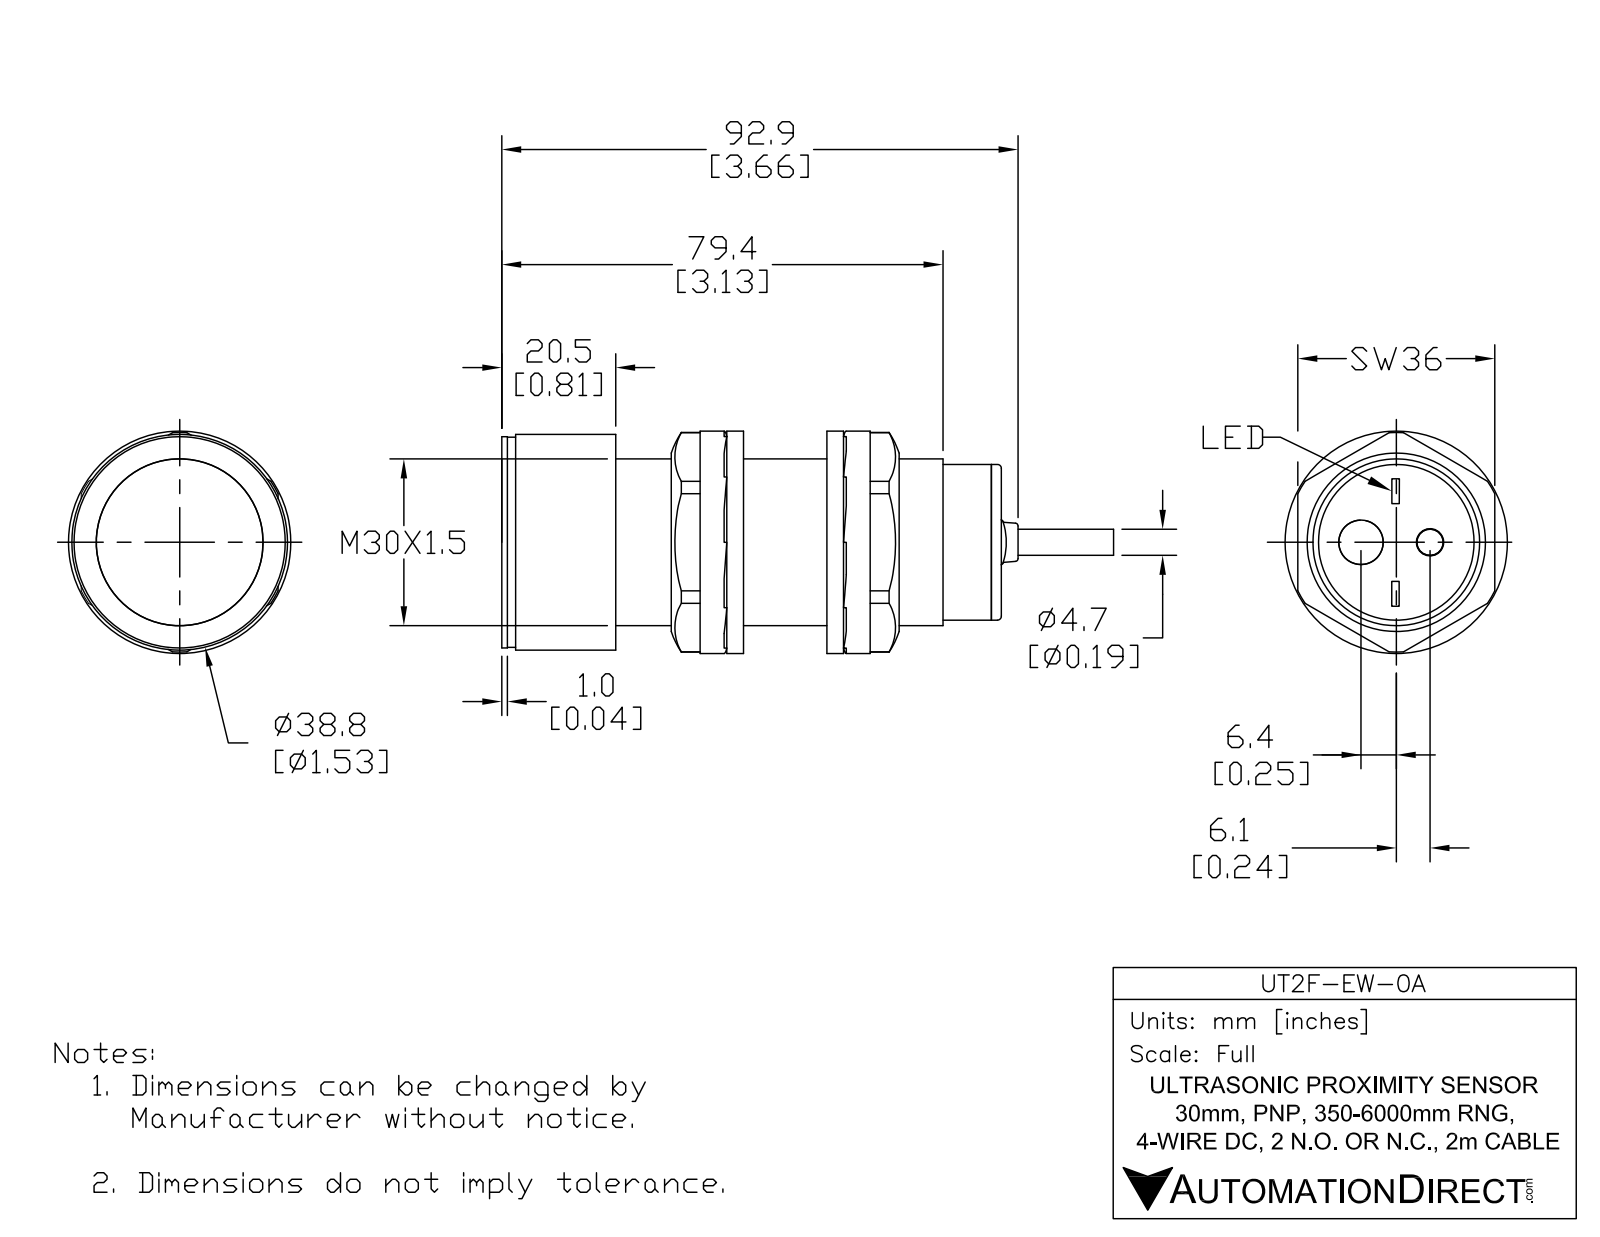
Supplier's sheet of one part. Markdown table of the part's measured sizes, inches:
| quantity | value |
| --- | --- |
| part name | UT2F-EW-0A |
| STEP written by | SolidWorks 2017 (AUTOMOTIVE_DESIGN) |
| units | inches |
| bodies | 5 solids, 49 faces (14 planar, 20 cylindrical, 15 other) |
| overall size | 5.043 × 1.528 × 1.528 |
| volume | 4.38 in³ |
| surface area | 24.02 in² |
| round holes (diameter × count) | 0.185 × 1, 0.315 × 1, 1.299 × 1 |
| round bosses / shafts (diameter × count) | 1.528 × 1, 1.488 × 1, 1.181 × 1, 1.102 × 1 |
| main face-to-face distances | 3.37, 0.059, 3.429, 0.767, 0.709, 2.661, 3.5, 3.441, 2.732, 0.071 |
| hole center spacings | 0.239, 0.25, 0.49 |
